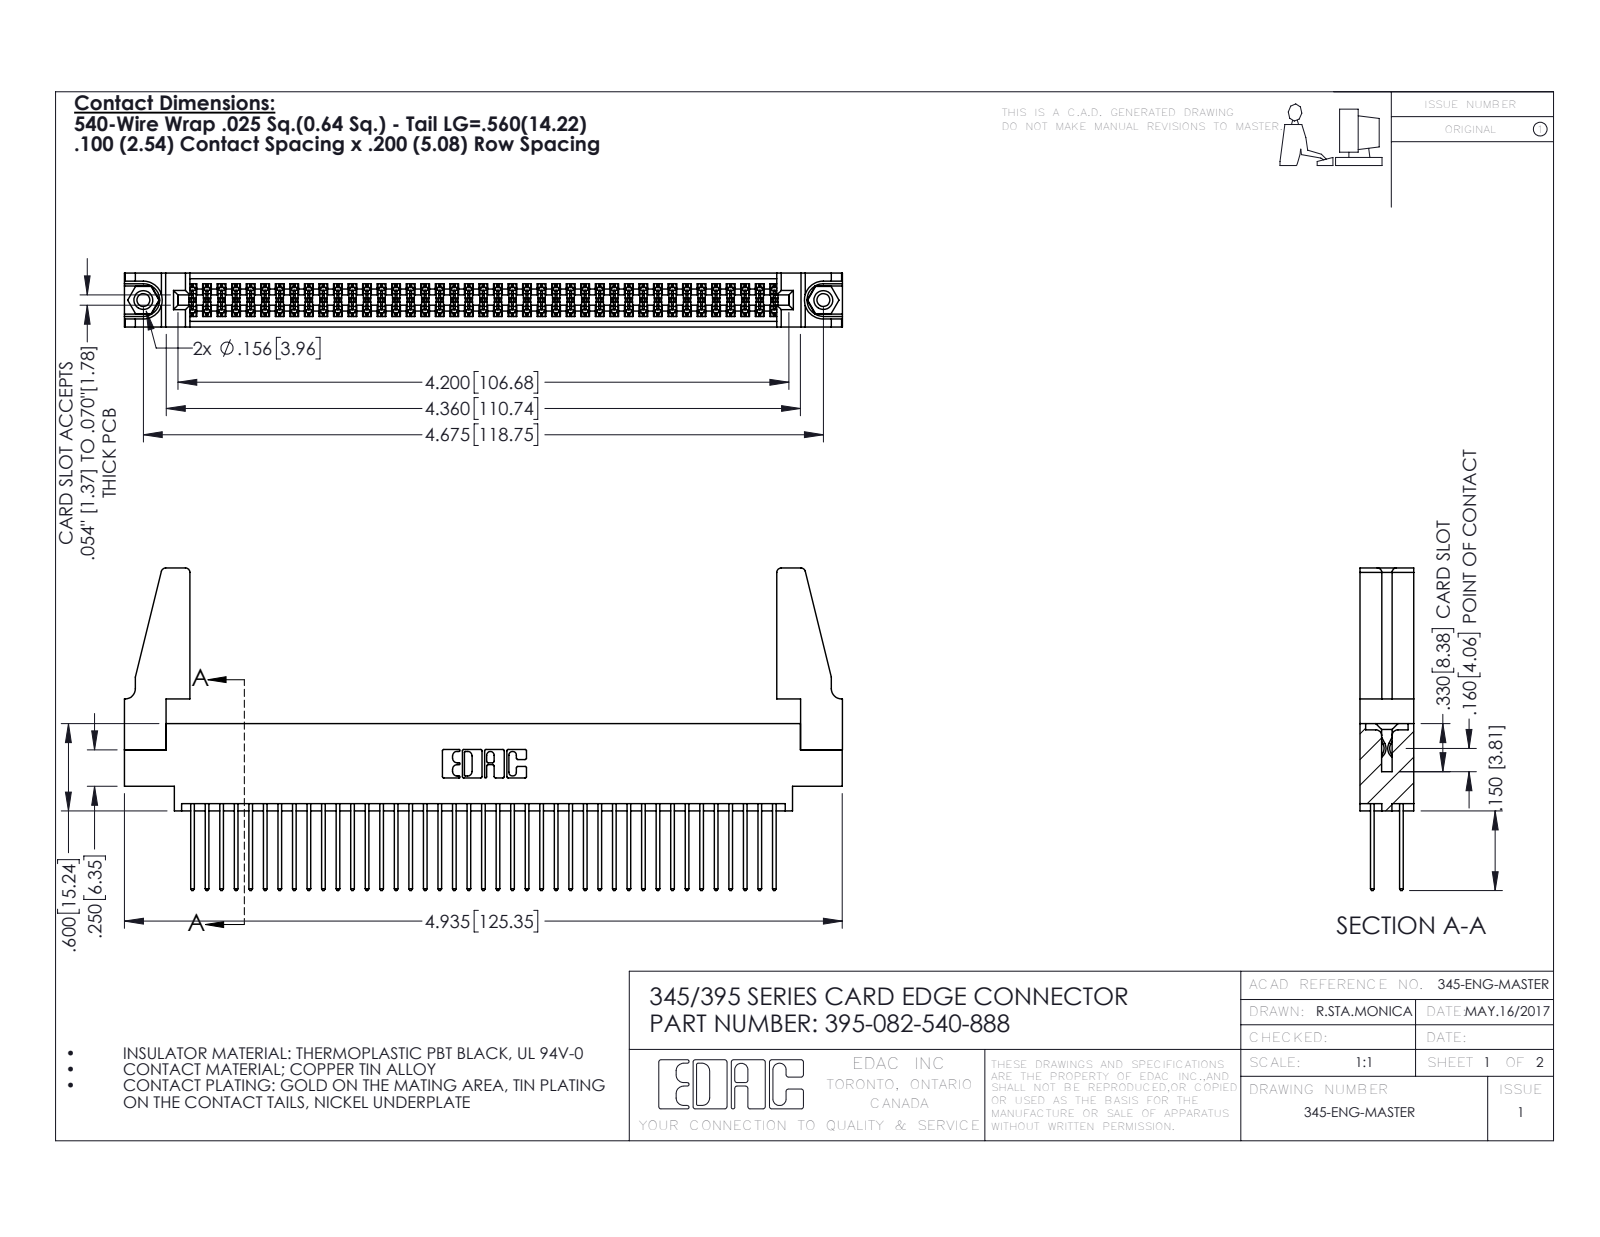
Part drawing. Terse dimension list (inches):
name: 395-082-540-888; 345-220-078_345-220-088; 345-292-001_345-293-140; 345-250-001_345-250-001-102 (+1 more)
written by: SolidWorks 2016 (CONFIG_CONTROL_DESIGN)
unit: in
bodies: 87 solids, 4354 faces (2862 planar, 1476 cylindrical, 16 other)
size: 4.936 × 2.217 × 0.37
volume: 0.953 in³; area: 35.6 in²
holes: 2× ⌀0.089, 2× ⌀0.125, 2× ⌀0.156, 1× ⌀0.064
bosses: 2× ⌀0.155
rounds: 123× R0.006, 82× R0.01, 22× R0.01, 8× R0.03, 6× R0.007, 6× R0.031, 3× R0.026, 2× R0.014
face distances: 0.072, 0.298, 0.37, 0.2, 0.098, 0.272, 0.025, 0.225, 0.175, 0.149
hole spacings: 0.27, 4.439, 4.675
